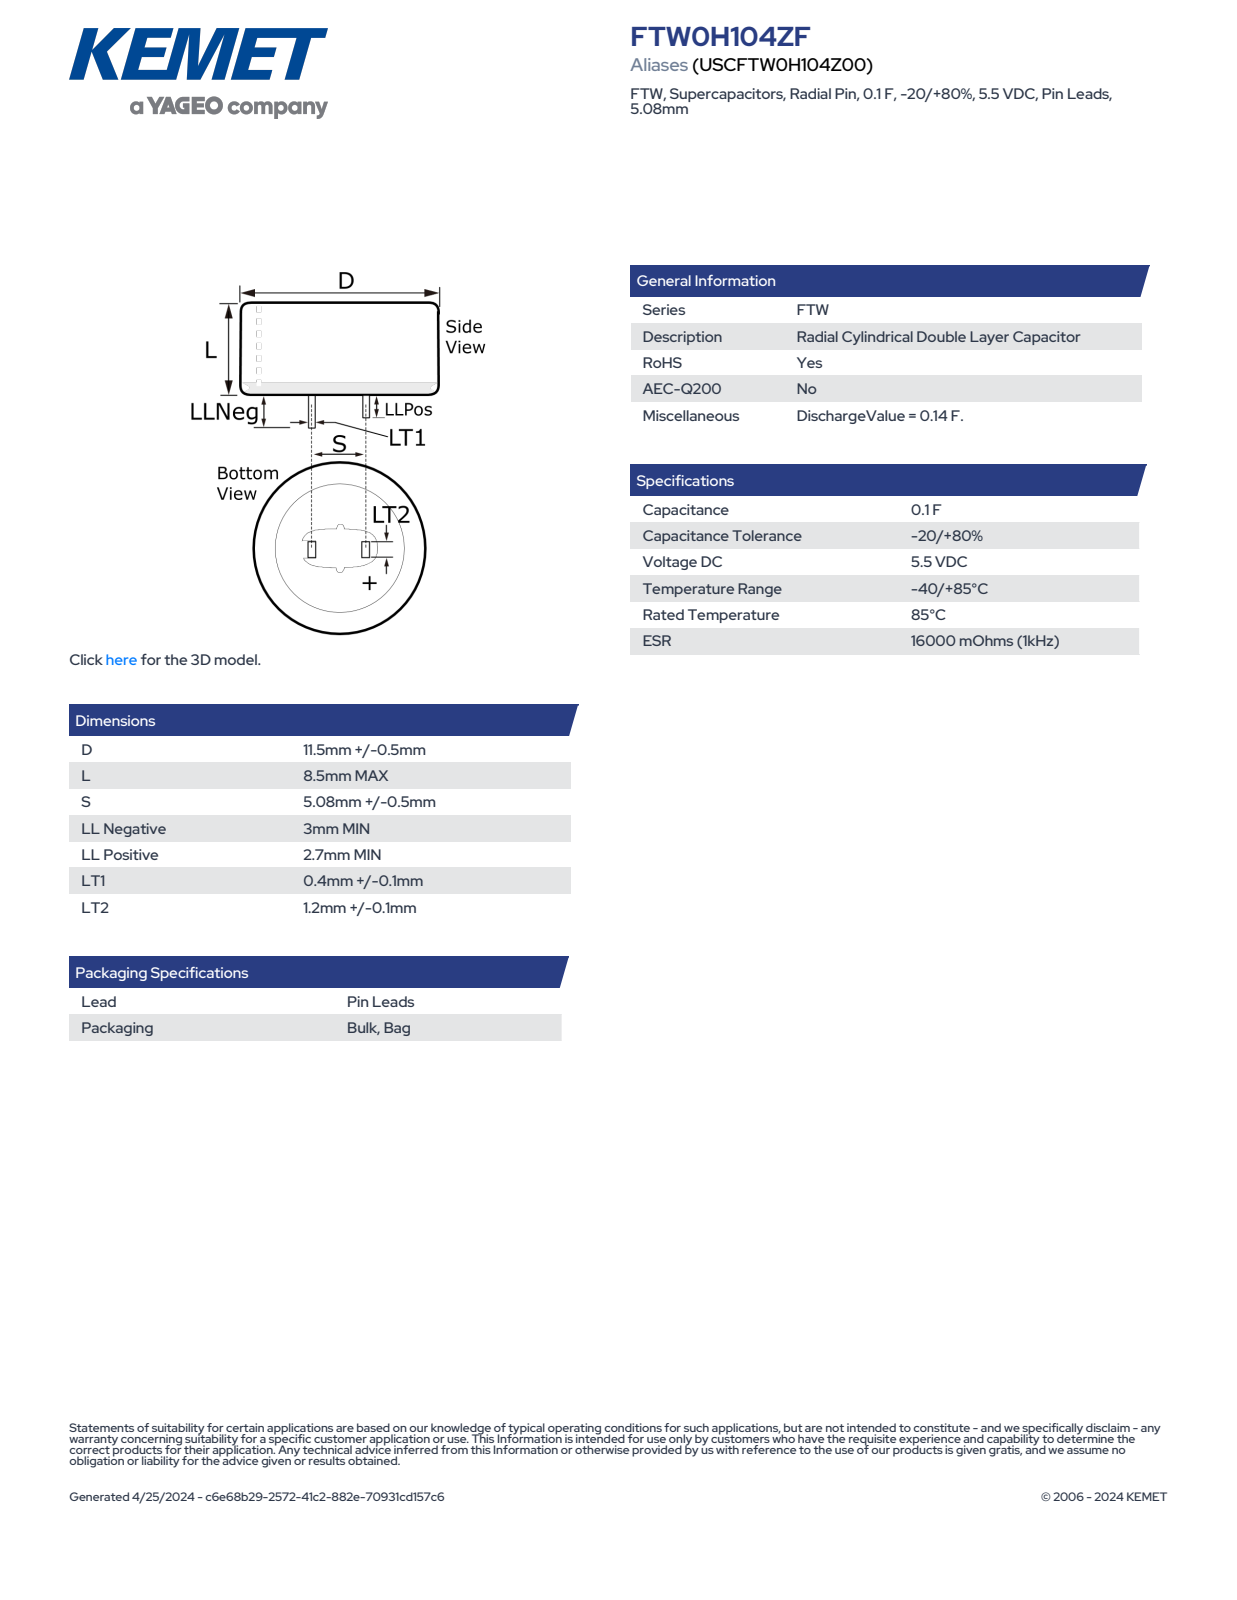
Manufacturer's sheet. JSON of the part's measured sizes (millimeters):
{"part_name": "CDR_LPLLN_D12L8.5S5.08LLNEG3LLPOS2.7LT10.5LT21.3", "step_written_by": "SolidWorks 2014 (AUTOMOTIVE_DESIGN)", "units": "millimeters", "bodies": {"solids": 1, "faces": 78, "planar": 70, "cylindrical": 4, "other": 4}, "overall_size": [12, 12, 11.5], "volume_mm3": 960, "surface_area_mm2": 550, "round_bosses_or_shafts": [[12, 1]], "partial_cylinders_radius": [[6.01, 1]], "face_to_face_distances": [8.5, 0.5, 5.08, 5.58, 4.58, 1.3, 2.7, 11.2, 3, 11.5]}
